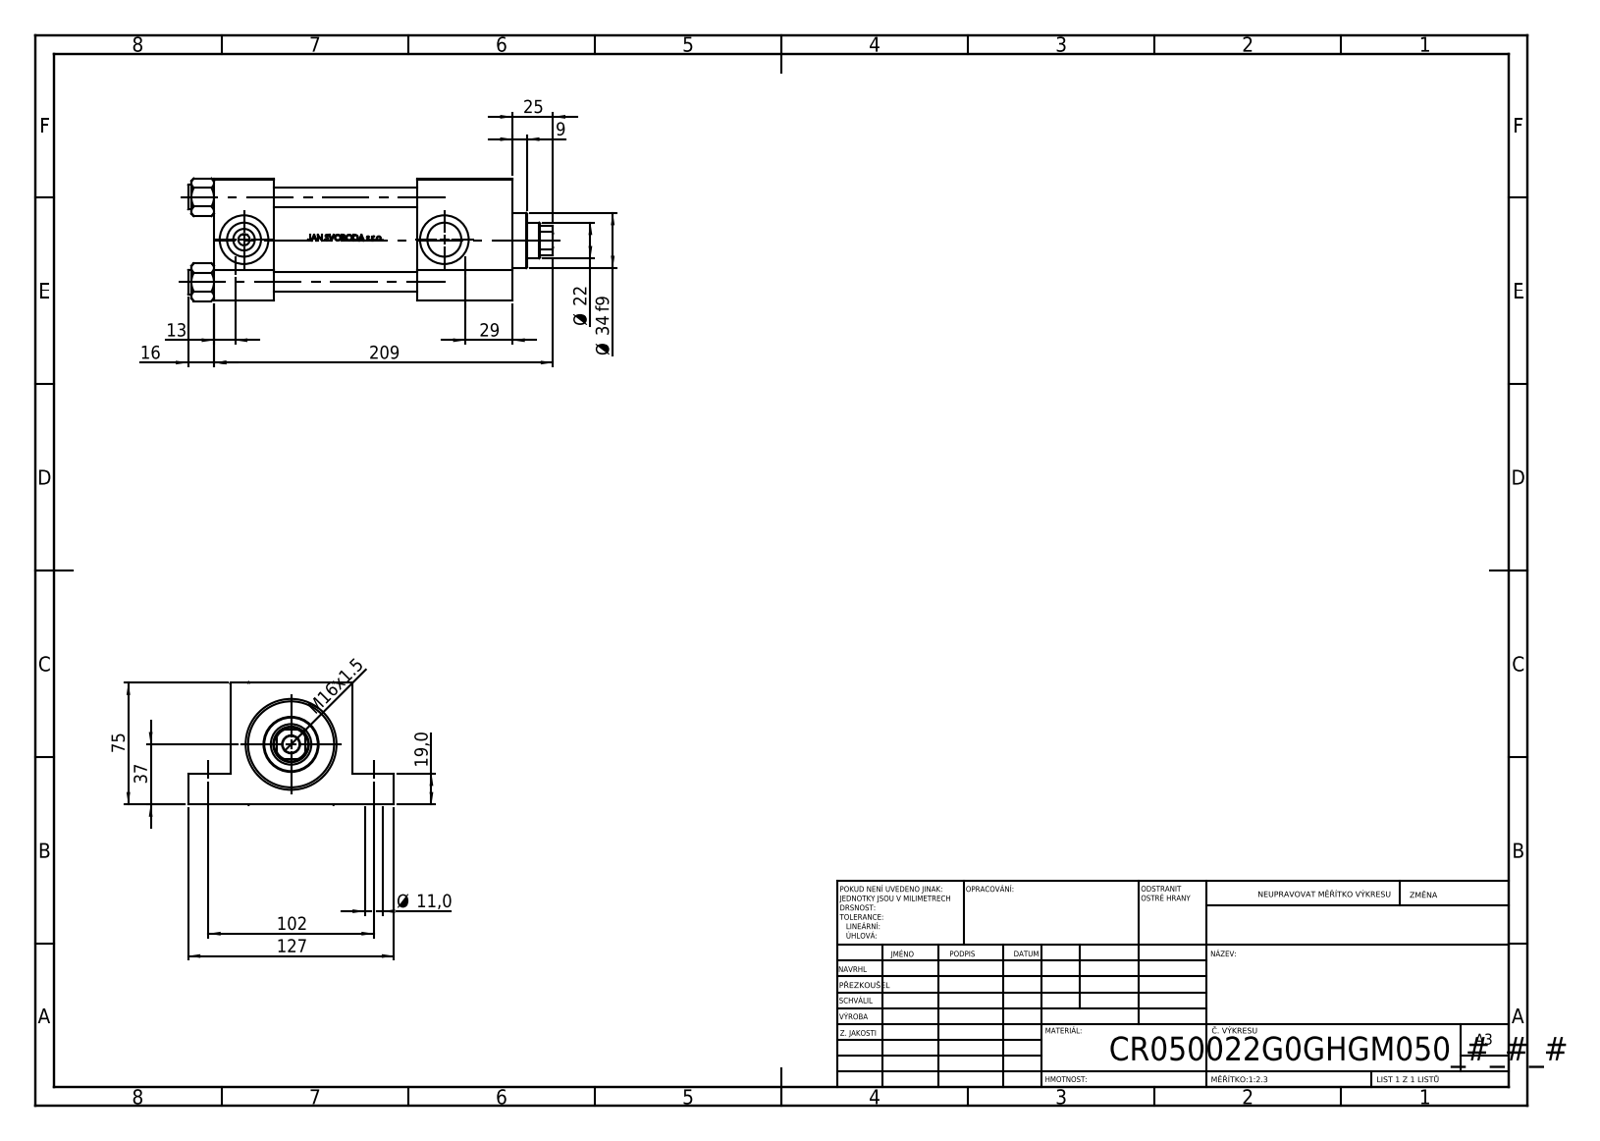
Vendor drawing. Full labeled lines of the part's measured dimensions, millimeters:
Part name (STEP PRODUCT): V215CR_G_TYCINKA; V215CR_VCP_G; V215_VC_A; V215CR_G_Body (+1 more)
STEP written by: SolidWorks 2019 (CONFIG_CONTROL_DESIGN)
Units: millimetres
Bodies: 11 solids, 1087 faces (431 planar, 124 cylindrical, 532 other)
Overall size (bounding box): 225 × 127 × 75.54
Volume: 795 809 mm³ · Surface area: 175 911 mm²
Round holes (diameter × count): ⌀11 ×4, ⌀12 ×4, ⌀7 ×2, ⌀20.96 ×2, ⌀30 ×2, ⌀10.5 ×1, ⌀22 ×1, ⌀25 ×1, ⌀41 ×1, ⌀50 ×1, ⌀53 ×1
Round bosses / shafts (diameter × count): ⌀15 ×4, ⌀56 ×1, ⌀34 ×1
Partial cylindrical surfaces — rounded edges, fillets, slot ends (radius × count): R10.5 ×1
Main face-to-face distances: 75, 37, 184, 147, 19, 56, 101, 125, 88, 59
Hole centre spacings: 52.3, 36.63, 37.34, 73.96, 102, 142, 174.84, 123.5
